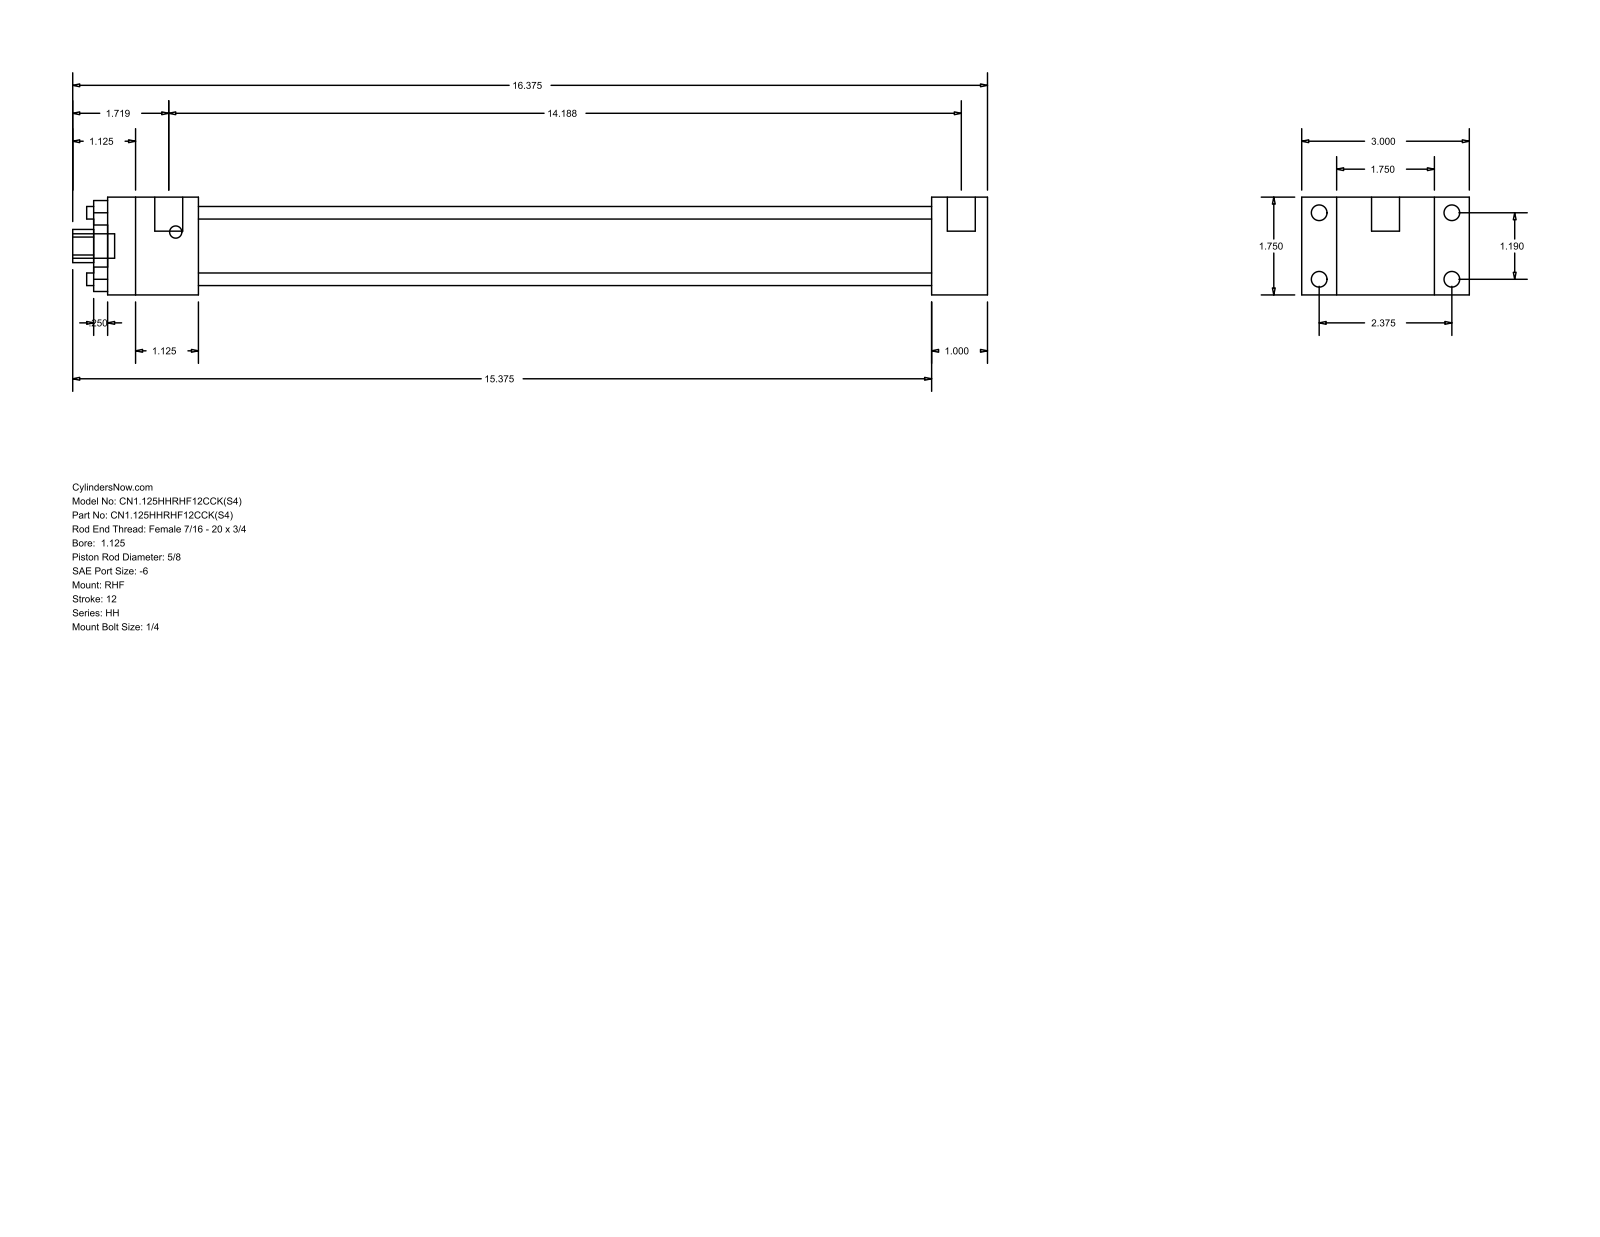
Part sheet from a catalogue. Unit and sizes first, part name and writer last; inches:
Units: inches
Overall size (bounding box): 16.375 × 3 × 1.75
Round holes (diameter × count): ⌀0.225 ×4, ⌀0.625 ×1, ⌀1.125 ×1, ⌀1.375 ×1
Round bosses / shafts (diameter × count): ⌀0.281 ×4, ⌀0.219 ×4, ⌀0.5 ×2, ⌀0.437 ×1
Partial cylindrical surfaces — rounded edges, fillets, slot ends (radius × count): R0.297 ×1
Main face-to-face distances: 1.75, 0.625, 2.375, 1, 3, 13.125, 14.125, 1.625, 14.75, 15.75
Hole centre spacings: 0.841, 1.19, 1.683
Bodies: 0 solids, 88 faces (60 planar, 28 cylindrical, 0 other)
Part name (STEP PRODUCT): HH_RHF__0112_0.625
STEP written by: GSSL Pune (CONFIG_CONTROL_DESIGN)
